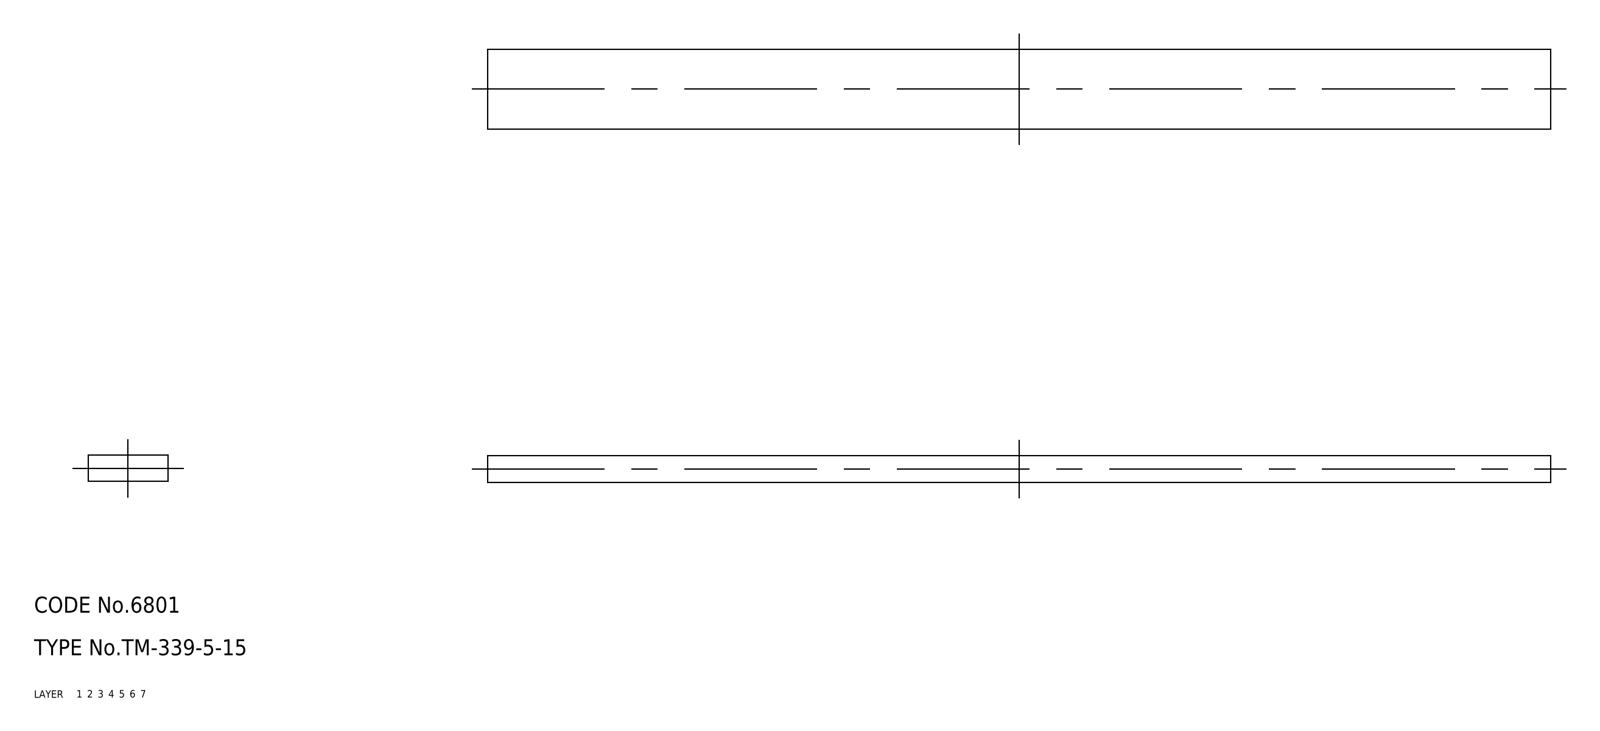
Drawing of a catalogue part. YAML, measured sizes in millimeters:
part_name: "rubber foam; TM_339_5_15"
step_written_by: "SolidWorks 2015 (AUTOMOTIVE_DESIGN)"
units: millimeters
bodies: {solids: 1, faces: 6, planar: 6, cylindrical: 0, other: 0}
overall_size: [200, 15, 5]
volume: 15000
surface_area: 8150
face_to_face_distances: [5, 15, 200]
